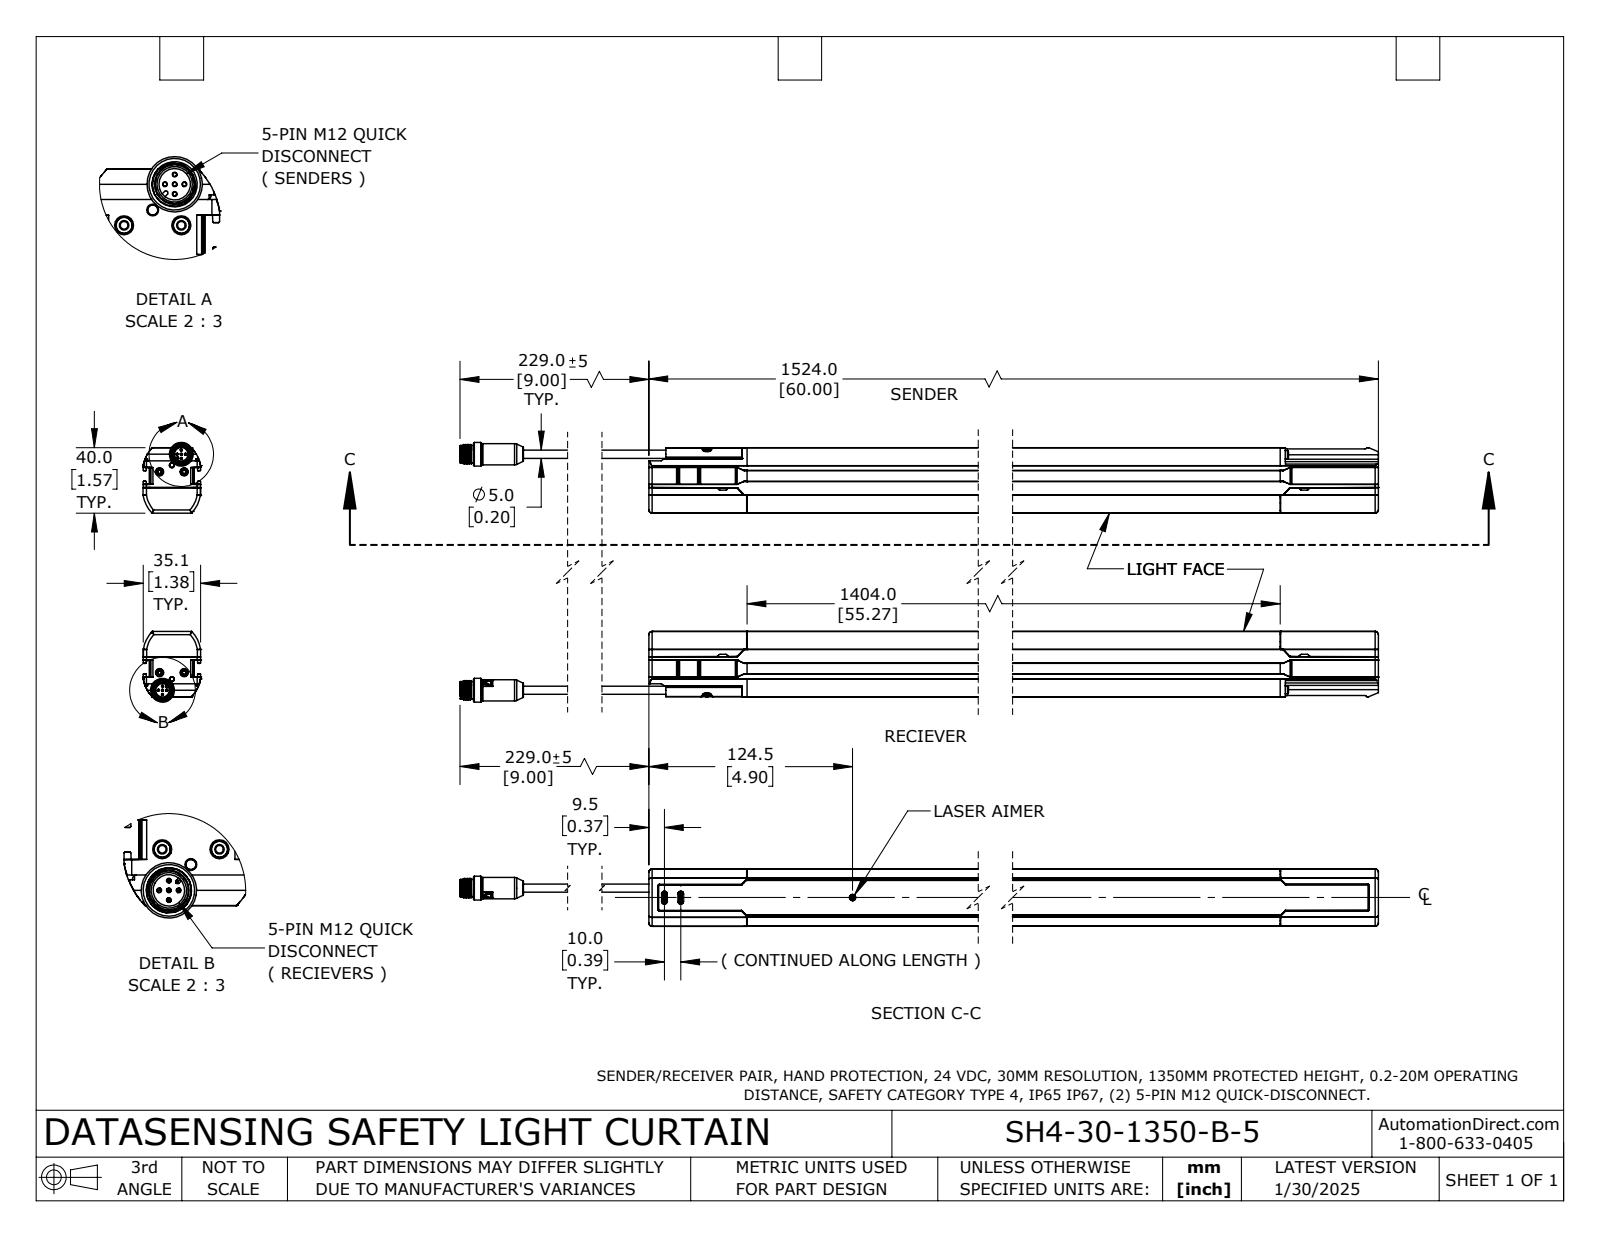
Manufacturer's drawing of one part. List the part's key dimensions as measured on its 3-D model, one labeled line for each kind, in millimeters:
Part name (STEP PRODUCT): SH4-30-1350-B-5
STEP written by: SolidWorks 2024 (AUTOMOTIVE_DESIGN)
Units: millimetres
Bodies: 4 solids, 2582 faces (1178 planar, 778 cylindrical, 626 other)
Overall size (bounding box): 1587.3 × 158.7 × 35.2
Volume: 3 207 000 mm³ · Surface area: 539 300 mm²
Round holes (diameter × count): ⌀2 ×4, ⌀3 ×4, ⌀5 ×4, ⌀2.5 ×2, ⌀2.5 ×2, ⌀2.6 ×2, ⌀2.6 ×2, ⌀2.8 ×2, ⌀8.3 ×2, ⌀9.7 ×2, ⌀10.3 ×2, ⌀10.8 ×2
Round bosses / shafts (diameter × count): ⌀5 ×10, ⌀1 ×10, ⌀2.2 ×8, ⌀4.4 ×4, ⌀14.5 ×2, ⌀13 ×2, ⌀10.6 ×2, ⌀9.5 ×2
Partial cylindrical surfaces — rounded edges, fillets, slot ends (radius × count): R0.3 ×164, R0.4 ×66, R0.5 ×50, R0.2 ×36, R0.8 ×20, R0.8 ×12, R2 ×12, R1.5 ×10
Main face-to-face distances: 38, 114.2, 31, 4, 76.2, 152.2, 35, 27.1, 117.7, 1.8
Hole centre spacings: 22, 132.5, 134.3, 10.9, 15, 17.1, 122.7, 123.6
